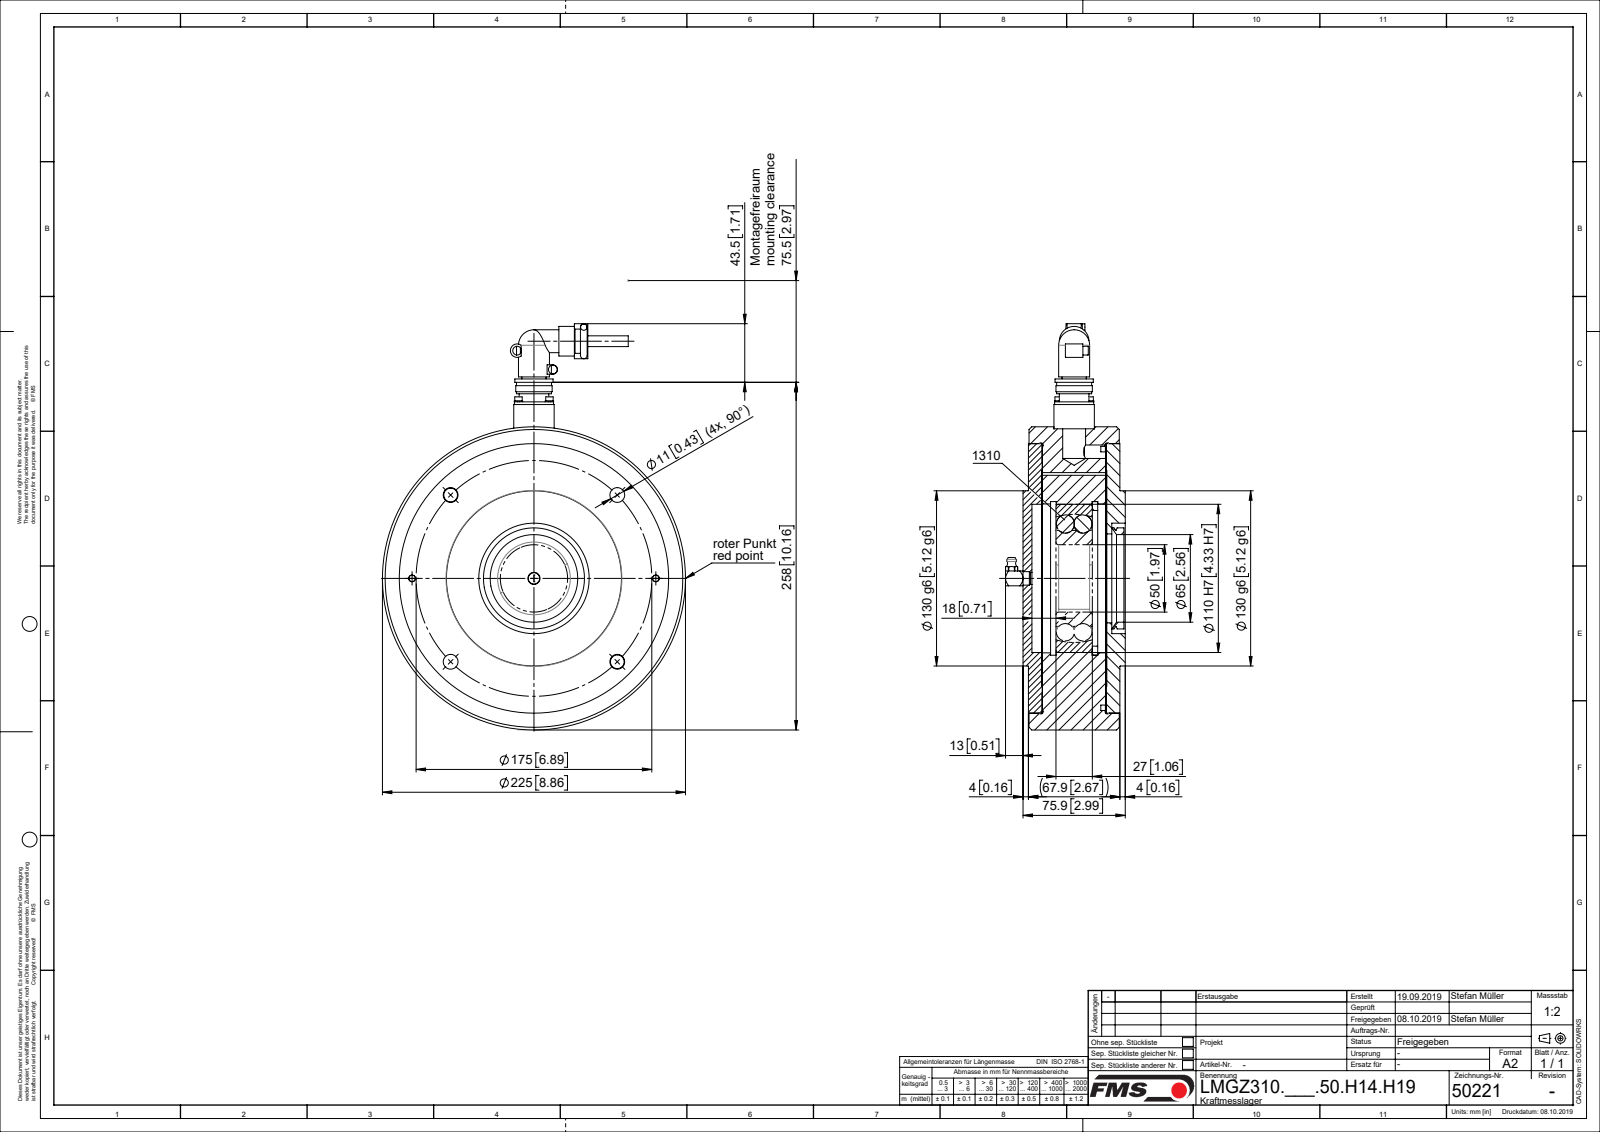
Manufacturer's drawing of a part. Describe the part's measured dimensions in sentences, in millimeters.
The part is named "ZEICHNUNG7; L50221; L4765504; TEIL1 (+8 more)". Its 3-D file was written by "Mechanical Desktop 2007 (CONFIG_CONTROL_DESIGN)". It is 21 solids with 432 faces: 131 planar, 236 cylindrical and 65 other. Overall it measures 301.5 by 225 by 90.4 millimeters. Its volume is 2 416 000 cubic millimeters and its surface area 394 168 square millimeters. Round holes: 6 of diameter 11, 4 of diameter 2.6, 4 of diameter 3.2, 4 of diameter 3.4, 4 of diameter 3.5, 4 of diameter 9, 2 of diameter 5, 2 of diameter 6.6, 1 of diameter 8.68, 1 of diameter 23, 1 of diameter 50, 1 of diameter 64. Round bosses or shafts: 4 of diameter 6.2, 4 of diameter 5.5, 4 of diameter 3, 3 of diameter 10, 2 of diameter 22, 2 of diameter 8, 2 of diameter 6.5, 2 of diameter 6. Partial cylindrical surfaces (rounded edges, fillets, slot ends): 2 of radius 2.5, 1 of radius 3.5, 1 of radius 5, 1 of radius 81, 1 of radius 86. The main face-to-face distances are 9.7, 47.25, 10.45, 10.75, 47.45, 10.2, 57.45, 57.7, 47, 10. The hole center spacings are 16.26, 23, 68.17, 87.5, 123.74, 164.45, 32.53, 90.5.
